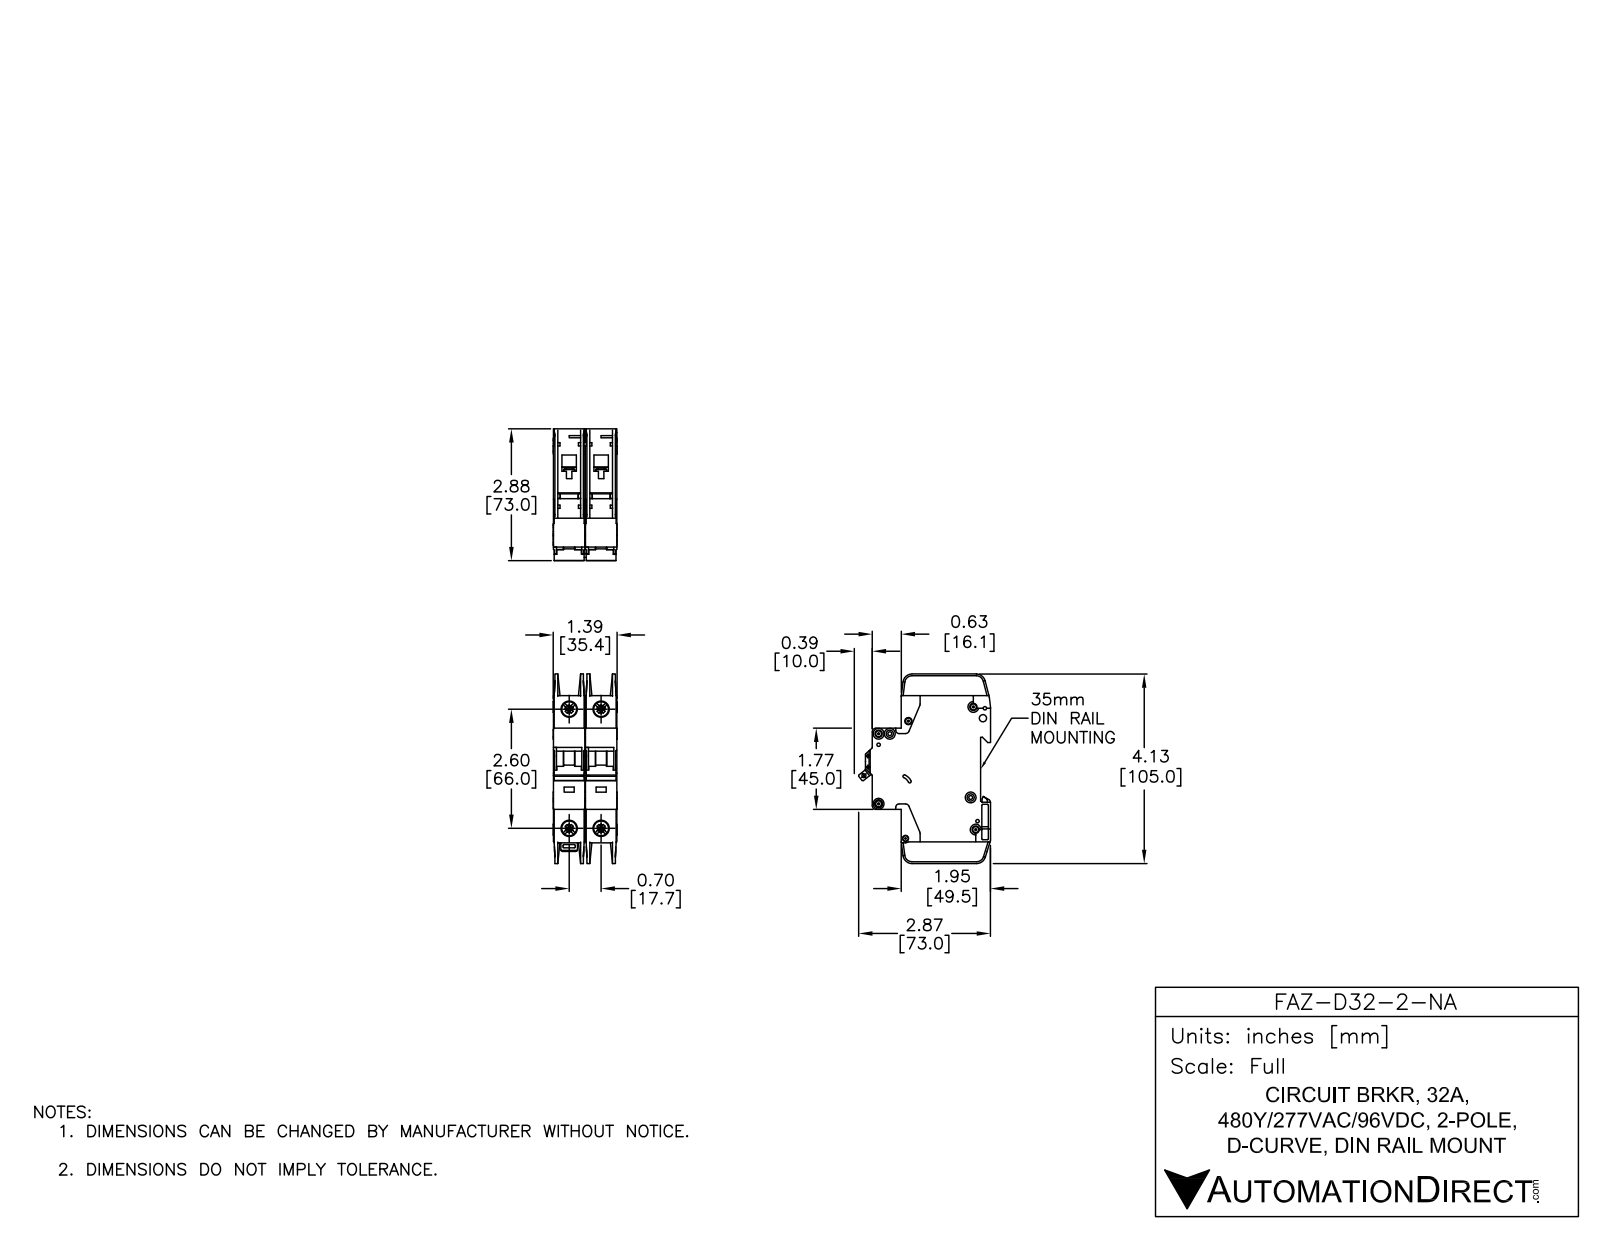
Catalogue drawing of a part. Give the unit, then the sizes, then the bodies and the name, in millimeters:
Units: millimetres
Overall size (bounding box): 105 × 73.04 × 35.4
Round holes (diameter × count): ⌀3.6 ×7, ⌀7.15 ×4, ⌀8.2 ×4, ⌀1.09 ×2, ⌀1.5 ×2, ⌀4 ×2, ⌀1.9 ×1, ⌀2.15 ×1, ⌀2.2 ×1, ⌀2.55 ×1, ⌀3.3 ×1, ⌀3.4 ×1
Round bosses / shafts (diameter × count): ⌀6 ×7, ⌀2.5 ×2
Partial cylindrical surfaces — rounded edges, fillets, slot ends (radius × count): R0.25 ×47, R0.5 ×24, R1 ×18, R2 ×12, R5 ×5, R1.8 ×4, R4 ×4, R0.2 ×2
Main face-to-face distances: 17.7, 17.5, 0.7, 15.05, 2.45, 1.75, 15.75, 13.3, 35.2, 17
Hole centre spacings: 6.2, 17.7, 66, 68.33, 5.19, 6.1, 8.19, 8.56
Volume: 155 390 mm³ · Surface area: 49 479 mm²
Bodies: 6 solids, 1568 faces (818 planar, 526 cylindrical, 224 other)
Part name (STEP PRODUCT): FAZ-D32-2-NA
STEP written by: SolidWorks 2014 (AUTOMOTIVE_DESIGN)
